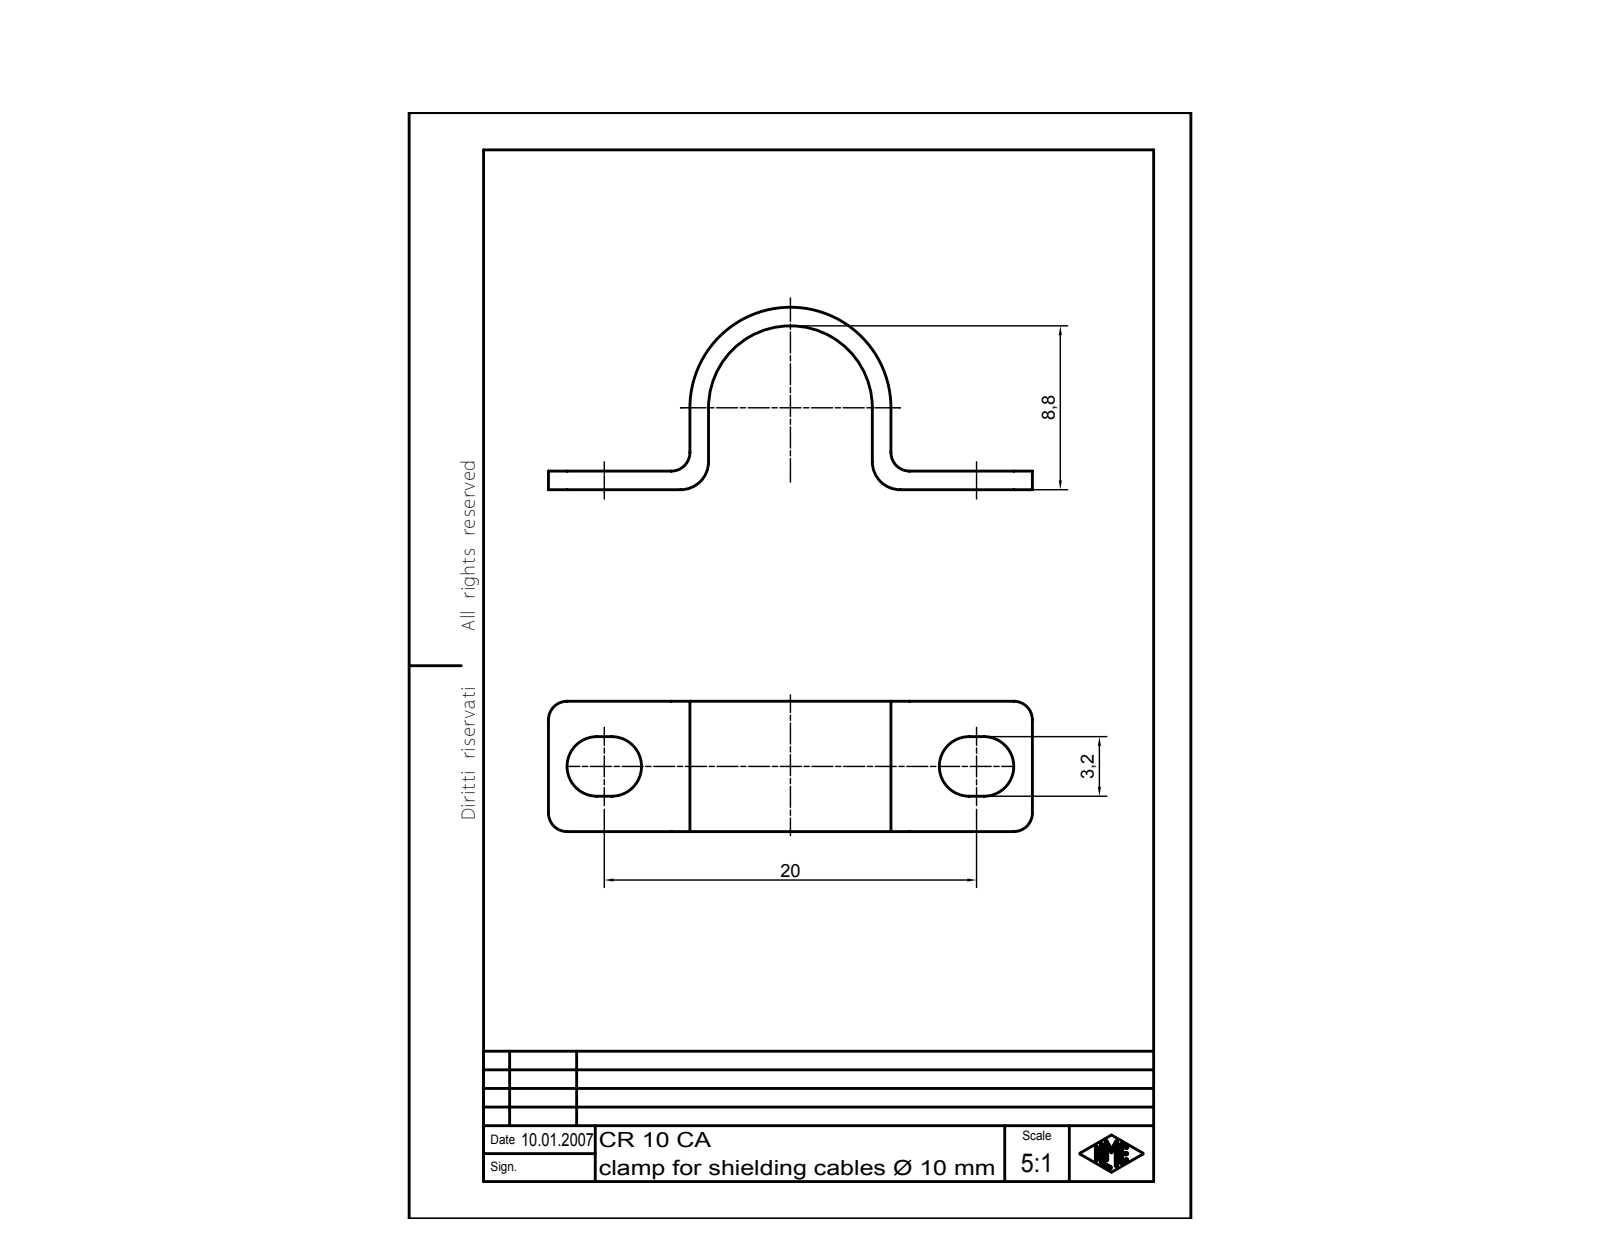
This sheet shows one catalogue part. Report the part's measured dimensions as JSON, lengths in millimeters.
{"part_name": "CR 10 CA", "step_written_by": "Autodesk Inventor 7 (AUTOMOTIVE_DESIGN)", "units": "millimeters", "bodies": {"solids": 1, "faces": 34, "planar": 14, "cylindrical": 16, "other": 4}, "overall_size": [26, 9.8, 7], "volume_mm3": 250, "surface_area_mm2": 606, "partial_cylinders_radius": [[1, 6], [1.5, 2], [1.6, 2], [4.4, 1], [5.4, 1]], "face_to_face_distances": [1, 7, 9.8, 8.8, 10.8, 7.6, 8.6, 17.4, 18.4, 26]}
